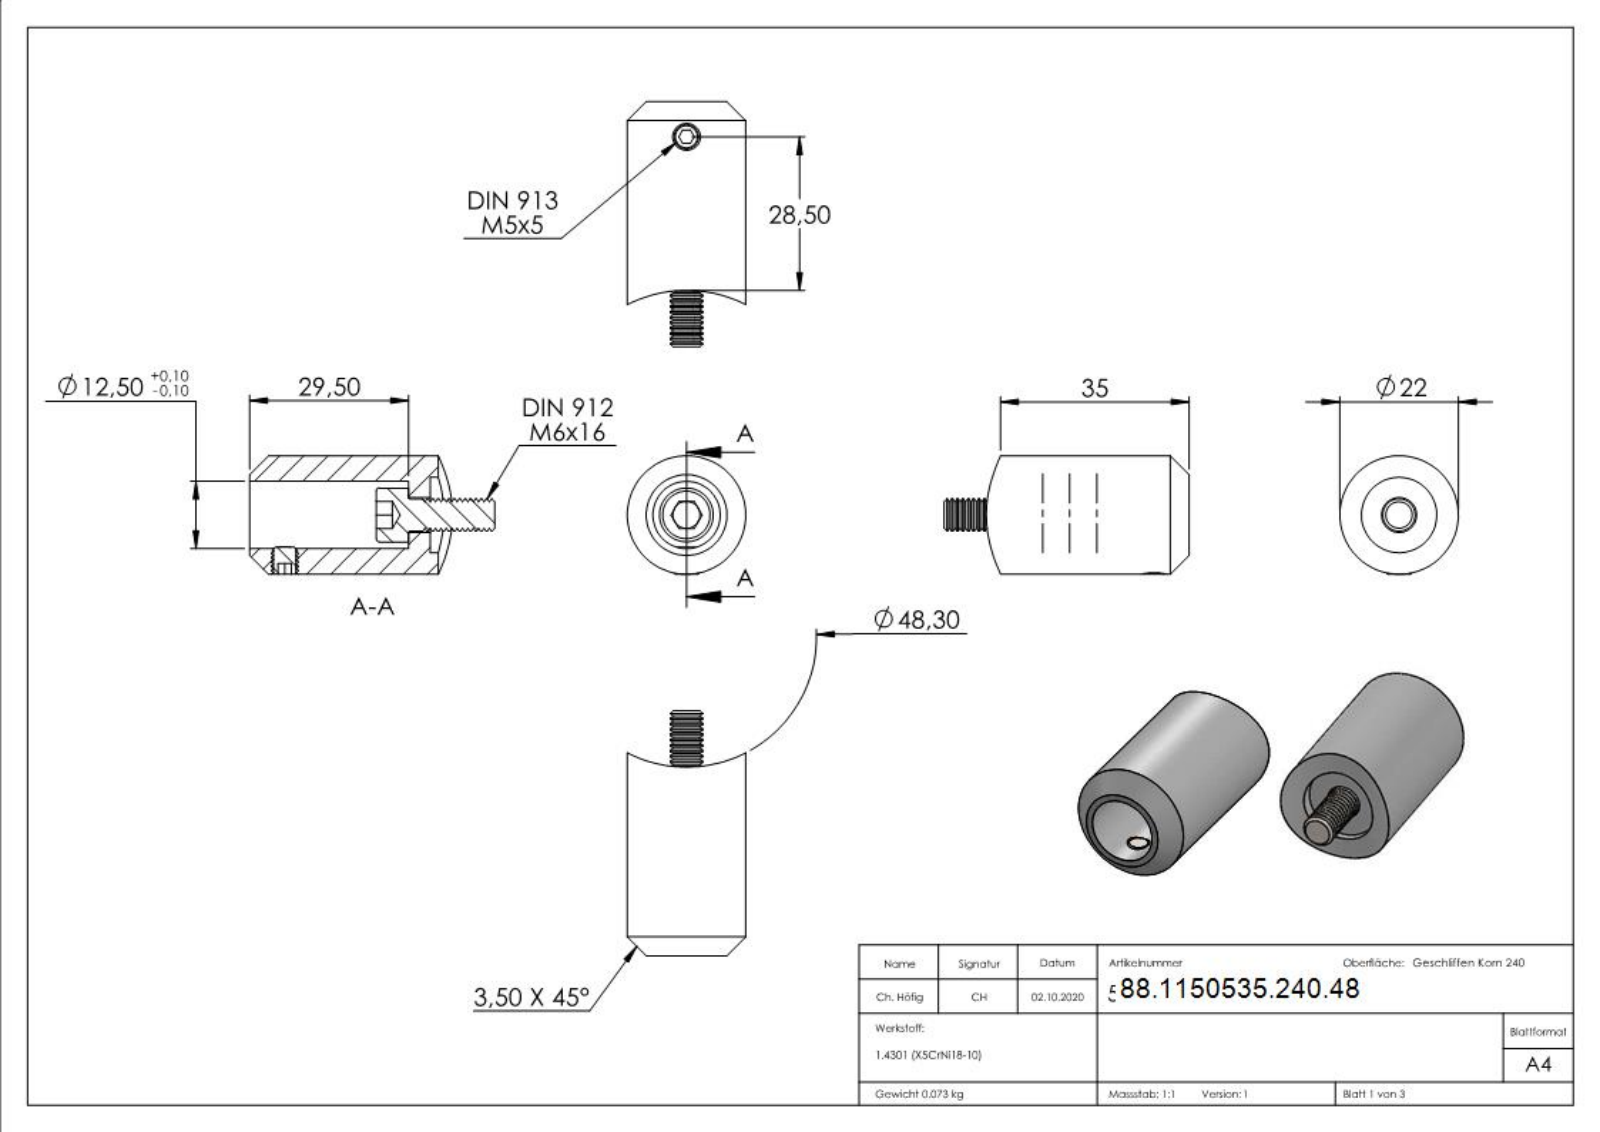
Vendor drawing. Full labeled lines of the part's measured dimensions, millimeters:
Part name (STEP PRODUCT): socket set screw flat point_din_DIN 913 - M5 x 5-S; socket head cap screw_din; socket set screw flat point_din; 50535-240-XX Teil1 (+3 more)
STEP written by: SolidWorks 2018 (CONFIG_CONTROL_DESIGN)
Units: millimetres
Bodies: 3 solids, 448 faces (162 planar, 67 cylindrical, 219 other)
Overall size (bounding box): 45.5 × 22 × 22
Volume: 9 945 mm³ · Surface area: 5 376 mm²
Round holes (diameter × count): ⌀4.2 ×1, ⌀6.5 ×1, ⌀12.5 ×1, ⌀14 ×1
Round bosses / shafts (diameter × count): ⌀22 ×1, ⌀10 ×1, ⌀6 ×1, ⌀5 ×1
Partial cylindrical surfaces — rounded edges, fillets, slot ends (radius × count): R24.15 ×1
Main face-to-face distances: 4, 33.5, 29.5, 6, 10, 23.5, 5.02, 12, 16, 22
